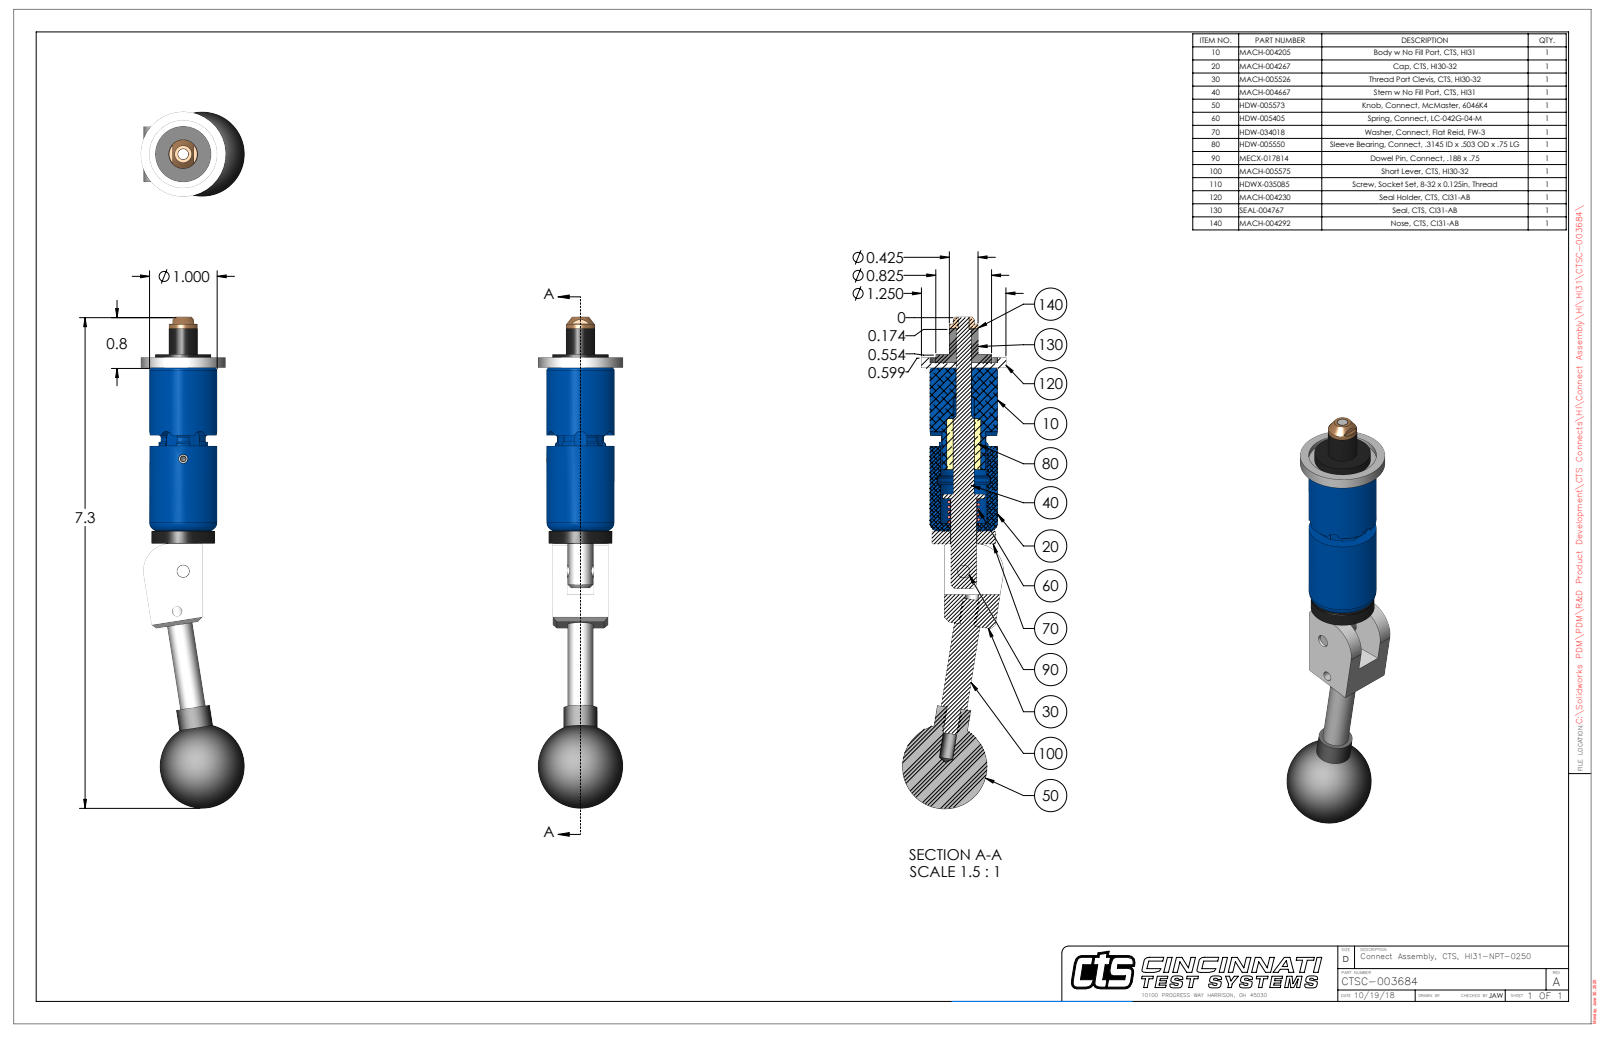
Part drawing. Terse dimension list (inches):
name: CTSC-003684
written by: SolidWorks 2023 (AUTOMOTIVE_DESIGN)
unit: in
bodies: 9 solids, 269 faces (102 planar, 111 cylindrical, 56 other)
size: 7.256 × 1.53 × 1.25
volume: 4.008 in³; area: 34.54 in²
holes: 2× ⌀0.201, 1× ⌀0.136, 1× ⌀0.15, 1× ⌀0.159, 1× ⌀0.189, 1× ⌀0.218, 1× ⌀0.228, 1× ⌀0.229, 1× ⌀0.385, 1× ⌀0.392, 1× ⌀0.688
bosses: 1× ⌀1.25, 1× ⌀1, 1× ⌀0.936, 1× ⌀0.825, 1× ⌀0.5, 1× ⌀0.427, 1× ⌀0.424, 1× ⌀0.38
rounds: 6× R0.093, 2× R0.029, 1× R0.375, 1× R0.4, 1× R0.458
face distances: 0.072, 0.21, 0.602, 2.48, 2.407, 0.812, 2.667, 2.595, 0.187, 0.391
hole spacings: 0.599, 1.658, 2.252
